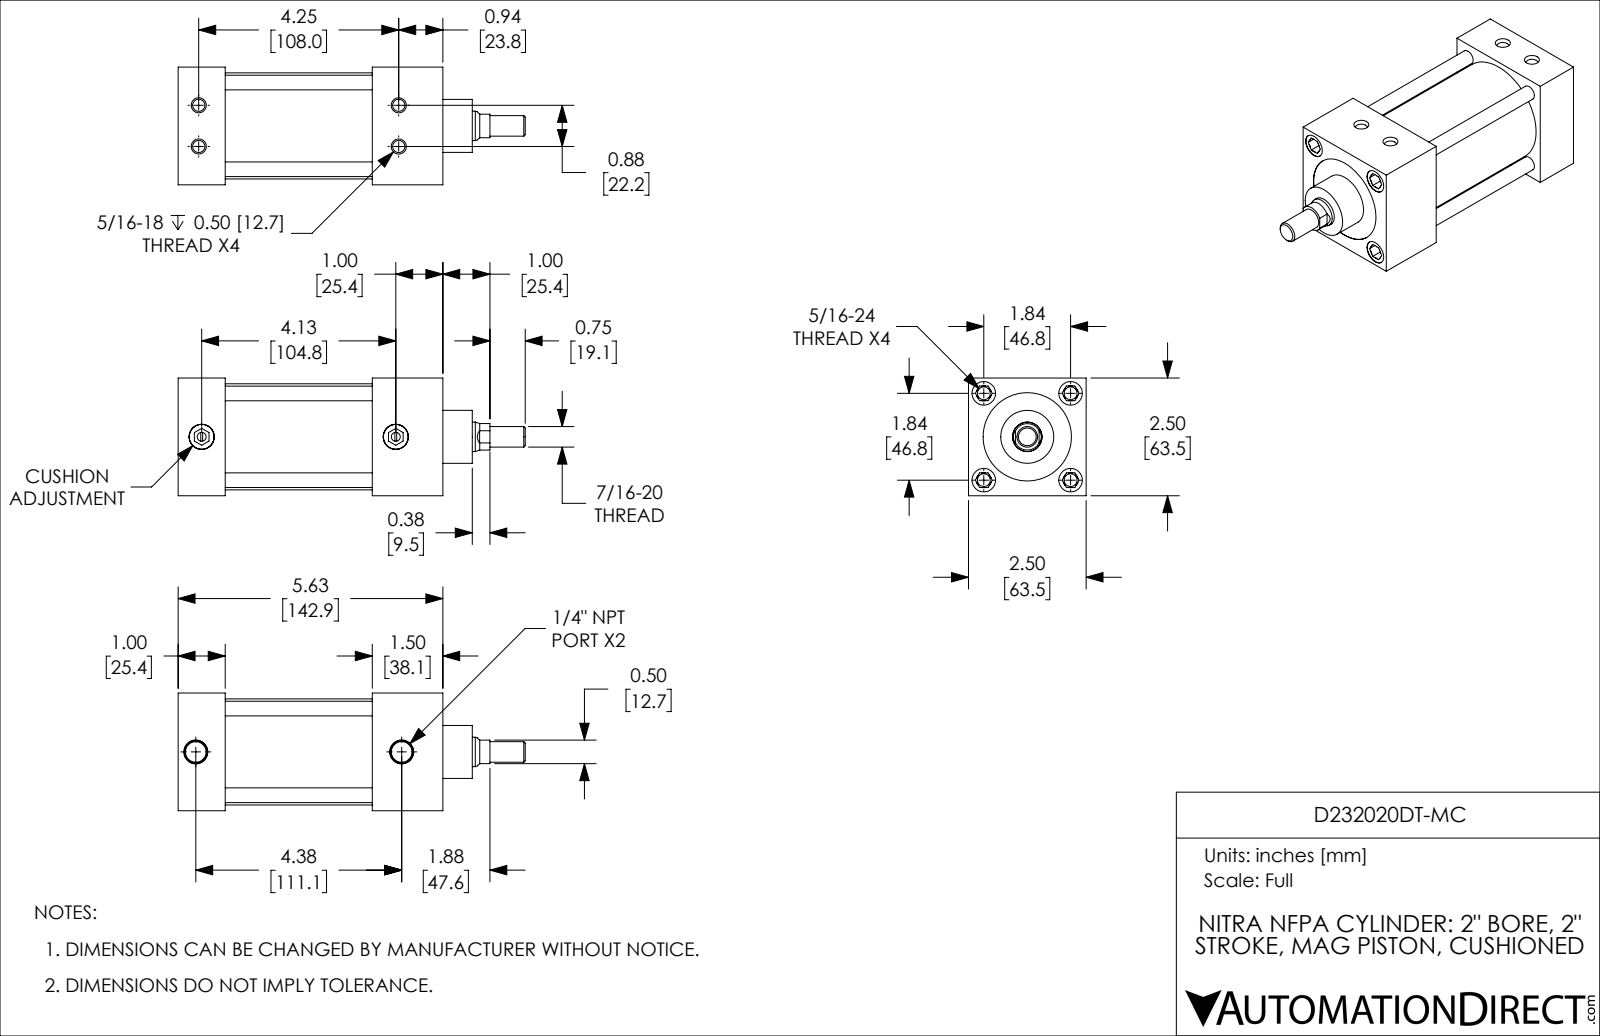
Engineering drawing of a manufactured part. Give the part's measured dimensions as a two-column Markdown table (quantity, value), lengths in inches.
| quantity | value |
| --- | --- |
| part name | D232020DT-MC_CUSHION; D232020DT-MC; D232020DT-MC_PISTON_KK1; D232020DT-MC_BODY |
| STEP written by | SolidWorks 2019 (CONFIG_CONTROL_DESIGN) |
| units | inches |
| bodies | 4 solids, 248 faces (90 planar, 78 cylindrical, 80 other) |
| overall size | 7.375 × 2.5 × 2.5 |
| volume | 23.32 in³ |
| surface area | 142.4 in² |
| round holes (diameter × count) | 0.272 × 7, 0.257 × 4, 0.5 × 4, 0.531 × 3, 0.19 × 2, 0.438 × 2, 0.626 × 1, 1.875 × 1, 2.001 × 1 |
| round bosses / shafts (diameter × count) | 0.312 × 4, 0.532 × 2, 2.251 × 1, 1.999 × 1, 1.125 × 1, 0.624 × 1, 0.437 × 1 |
| partial cylindrical surfaces (radius × count) | 0.281 × 1 |
| main face-to-face distances | 2.5, 1, 4.125, 3.125, 2.125, 1.125, 2, 5.625, 4.625, 3.5 |
| hole center spacings | 1.84, 1.844, 1.301, 0.441, 0.443, 0.875, 1.304, 2.602 |
